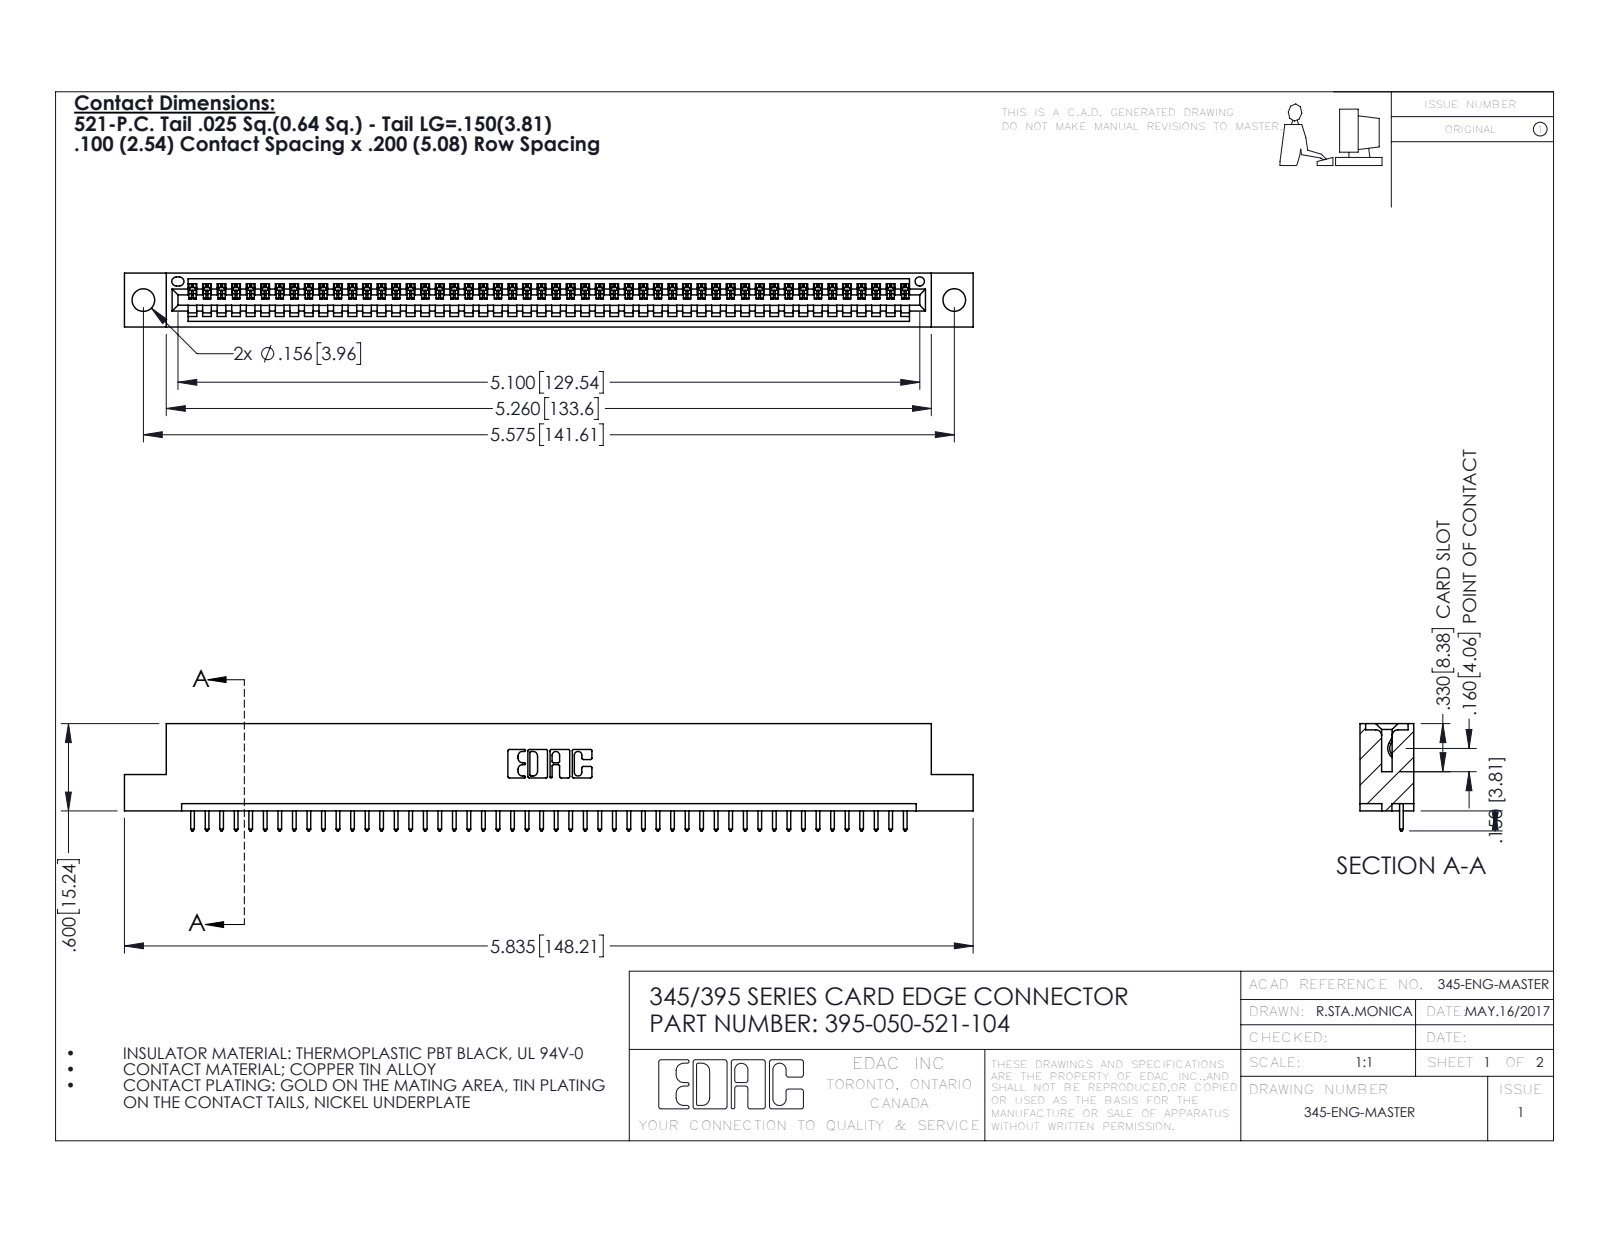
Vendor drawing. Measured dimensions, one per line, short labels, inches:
name: 395-050-521-104; 345 Part_Flush Mounting Lugs - 0.156 Dia-TH; 345-292-001_345-293-121
written by: SolidWorks 2016 (CONFIG_CONTROL_DESIGN)
unit: in
bodies: 51 solids, 3026 faces (2080 planar, 946 cylindrical, 0 other)
size: 5.835 × 0.737 × 0.37
volume: 0.849 in³; area: 27.67 in²
holes: 2× ⌀0.156, 1× ⌀0.064
rounds: 100× R0.006, 100× R0.01, 22× R0.01, 6× R0.007, 6× R0.031, 3× R0.026, 2× R0.031, 2× R0.04
face distances: 0.298, 0.072, 0.37, 0.2, 0.098, 0.272, 0.025, 0.225, 0.149, 0.072
hole spacings: 0.27, 5.339, 5.575
